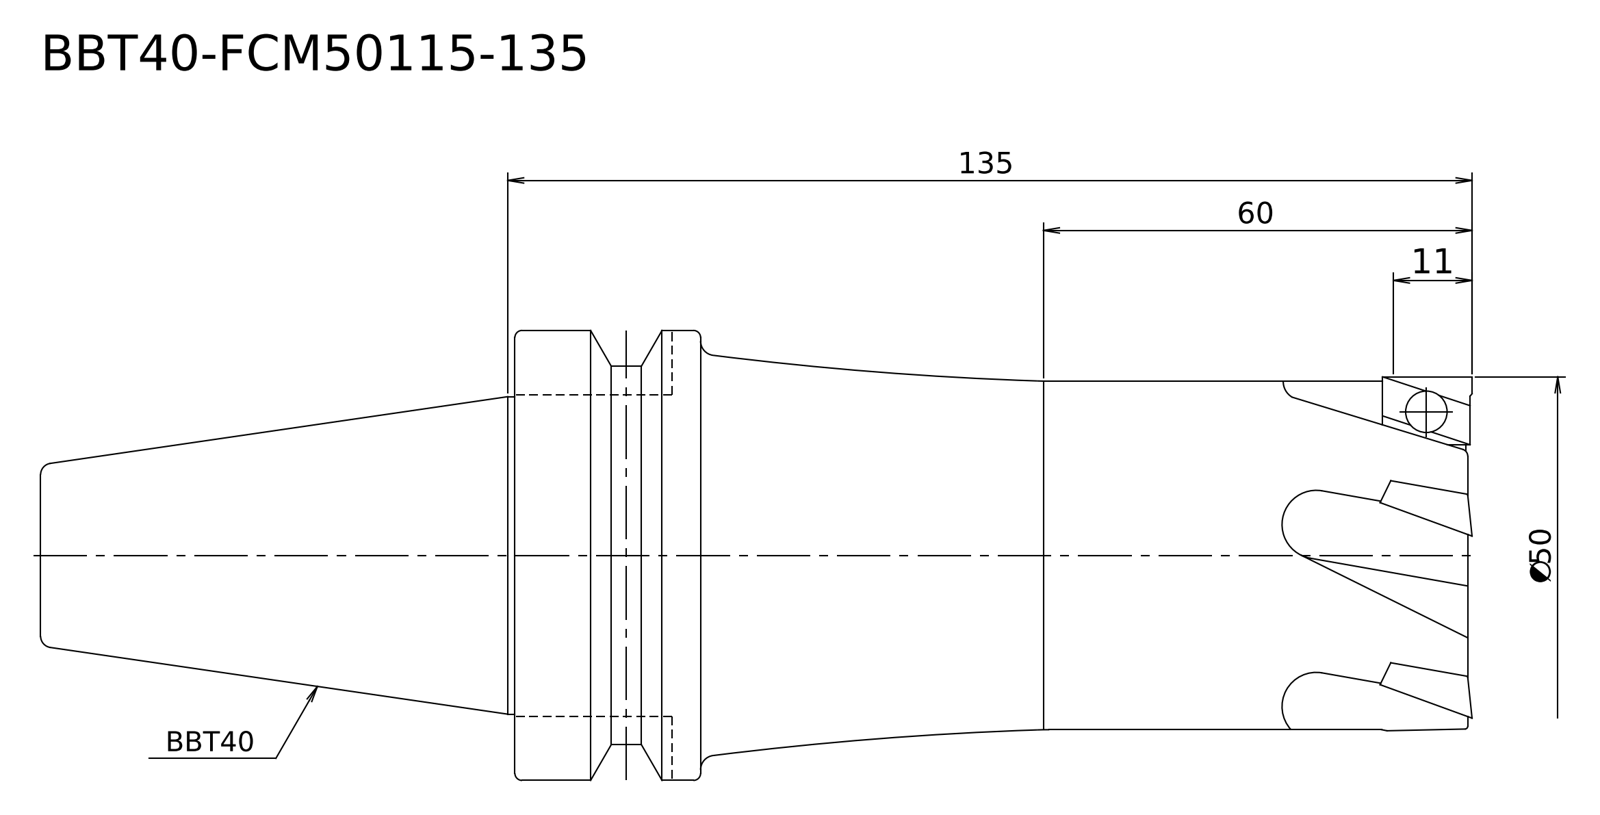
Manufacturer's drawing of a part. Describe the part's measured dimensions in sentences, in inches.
Its 3-D file was written by "Kubotek KeyCreator V8.5.1 (14335) (CONFIG_CONTROL_DESIGN)". It is 1 solid with 17 faces: 4 planar, 6 cylindrical and 7 other. Overall it measures 7.89 by 2.48 by 2.48 inches. Its volume is 21.84 cubic inches and its surface area 54.35 square inches. Round bosses or shafts: 1 of diameter 2.48, 1 of diameter 2.087, 1 of diameter 1.969, 1 of diameter 1.921, 1 of diameter 1.75. The main face-to-face distances are 5.276, 7.89, 2.614, 4.252, 1.024, 3.638.
